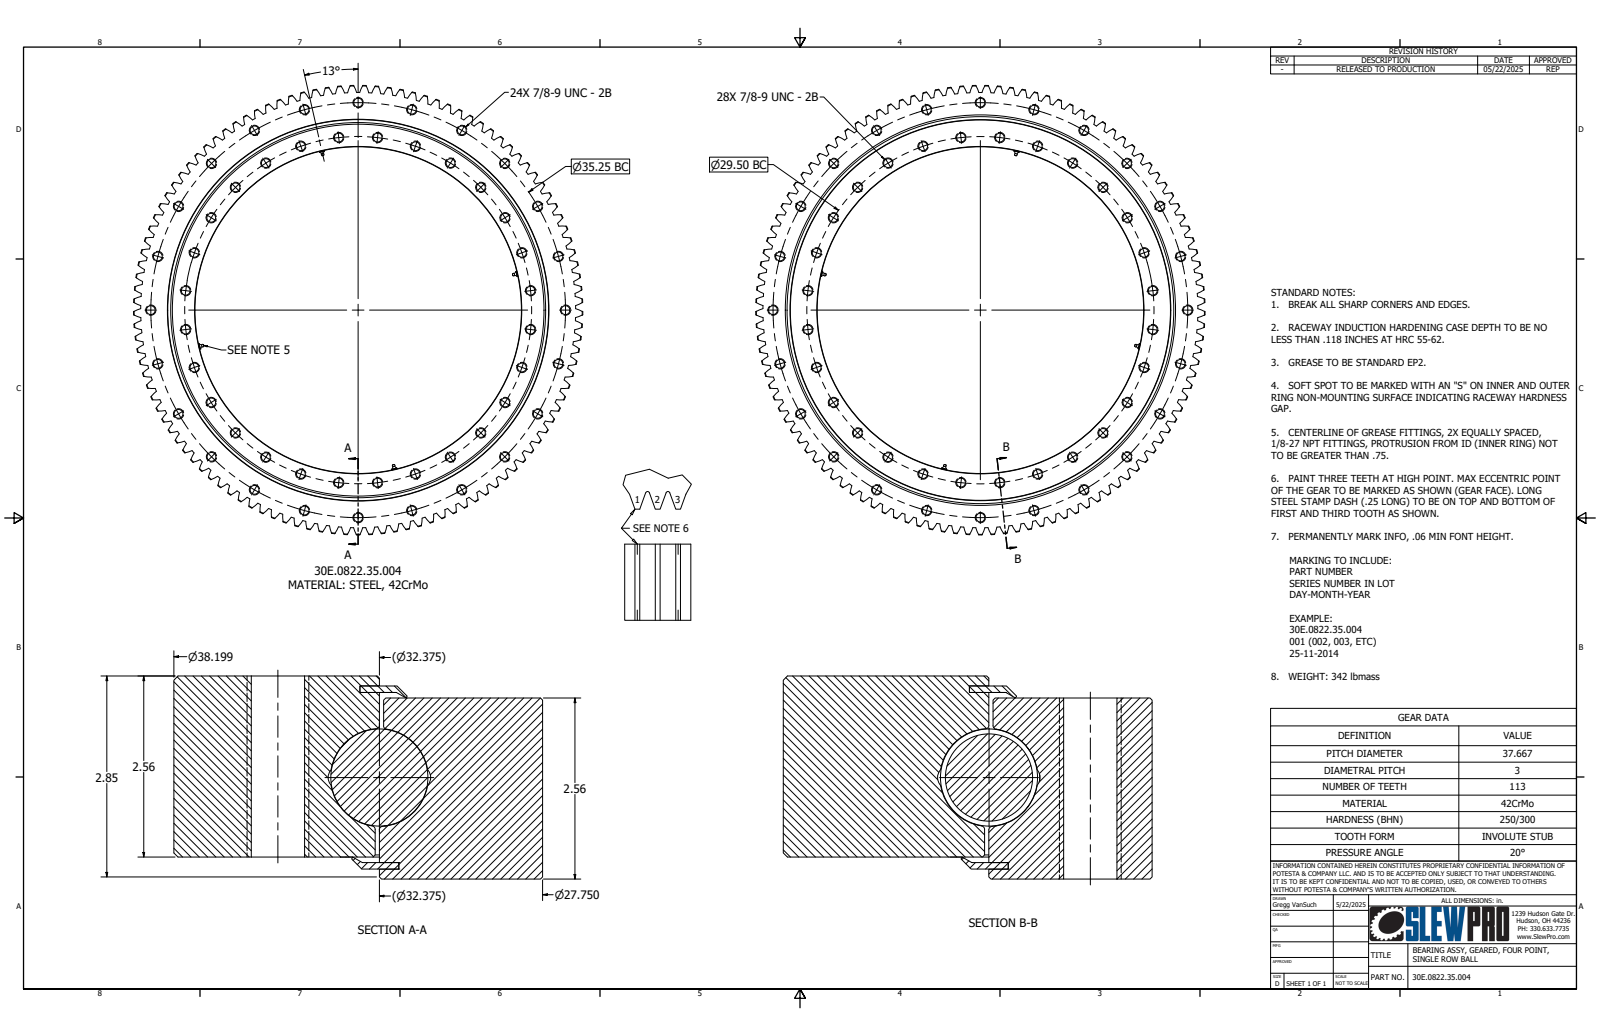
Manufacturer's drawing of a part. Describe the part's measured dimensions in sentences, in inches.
The part is named "30E.0822.35.004; Spur Gears1; 1_8 NPT Fitting". Its 3-D file was written by "Autodesk Inventor 2026 (AUTOMOTIVE_DESIGN)". It is 10 solids with 1011 faces: 58 planar, 528 cylindrical and 425 other. Overall it measures 38.198 by 38.195 by 2.875 inches. Its volume is 1 205 cubic inches and its surface area 3 531 square inches. Round holes: 52 of diameter 0.755, 4 of diameter 0.1, 1 of diameter 1.502, 1 of diameter 27.75, 1 of diameter 31.825, 1 of diameter 32.495, 1 of diameter 32.926. Round bosses or shafts: 1 of diameter 32.925, 1 of diameter 32.375, 1 of diameter 32.255, 1 of diameter 31.824, 1 of diameter 1.5. Partial cylindrical surfaces (rounded edges, fillets, slot ends): 226 of radius 3.586, 1 of radius 18.483, 1 of radius 19.099. The main face-to-face distances are 2.563, 0.312, 2.875, 2.251, 2.501, 0.093, 0.141, 2.734, 0.171, 2.422. The hole center spacings are 9.743, 12.8, 3.303, 6.565, 14.75, 20.86, 15.695, 18.393.
